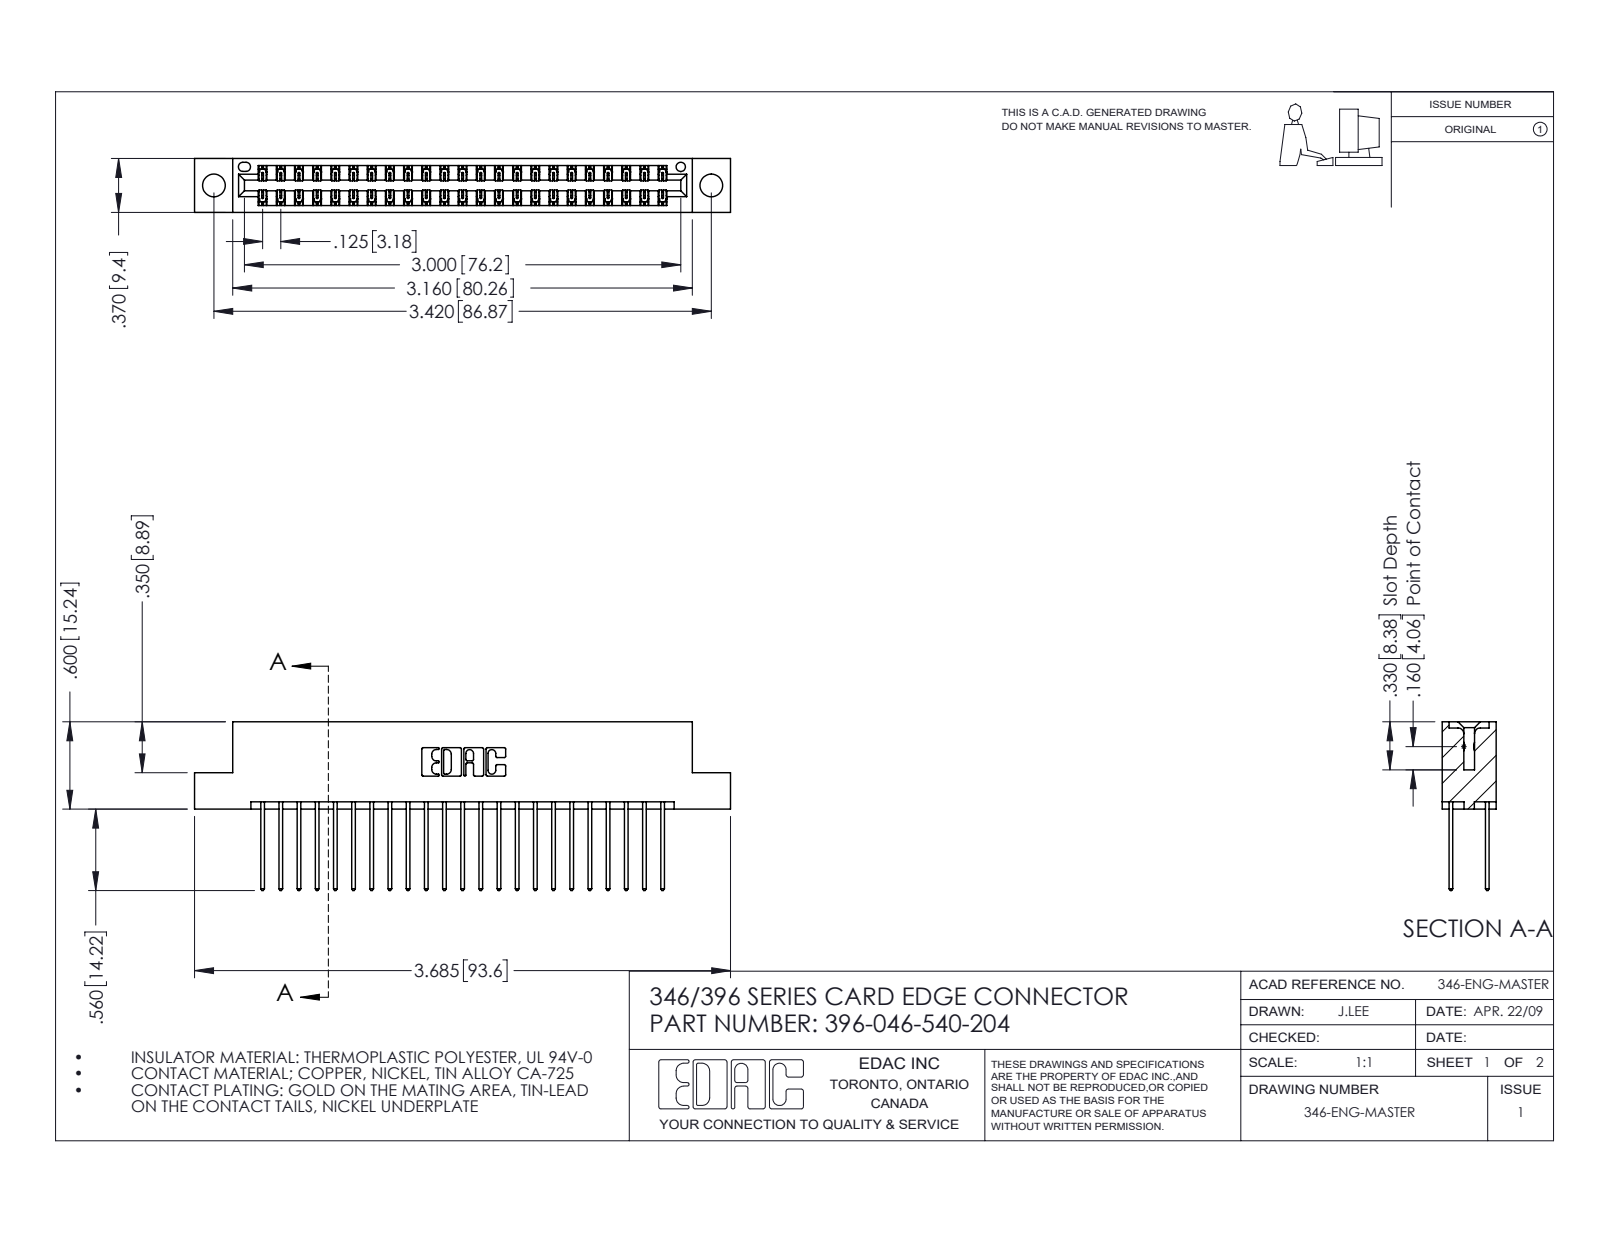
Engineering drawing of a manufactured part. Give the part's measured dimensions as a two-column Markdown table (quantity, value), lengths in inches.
| quantity | value |
| --- | --- |
| part name | 396-046-540-204; 346 Part_Flush Mounting Lugs - 0.156 Dia-TH; 345-292-001_345-293-140 |
| STEP written by | SolidWorks 2016 (CONFIG_CONTROL_DESIGN) |
| units | inches |
| bodies | 47 solids, 2514 faces (1686 planar, 828 cylindrical, 0 other) |
| overall size | 3.685 × 1.16 × 0.37 |
| volume | 0.553 in³ |
| surface area | 19.84 in² |
| round holes (diameter × count) | 0.156 × 2, 0.064 × 1 |
| partial cylindrical surfaces (radius × count) | 0.006 × 69, 0.01 × 46, 0.01 × 22, 0.007 × 6, 0.031 × 6, 0.026 × 3, 0.014 × 2, 0.022 × 2 |
| main face-to-face distances | 0.048, 0.322, 0.25, 0.072, 0.298, 0.025, 0.37, 0.275, 0.148, 0.222 |
| hole center spacings | 0.246, 3.212, 3.42 |
